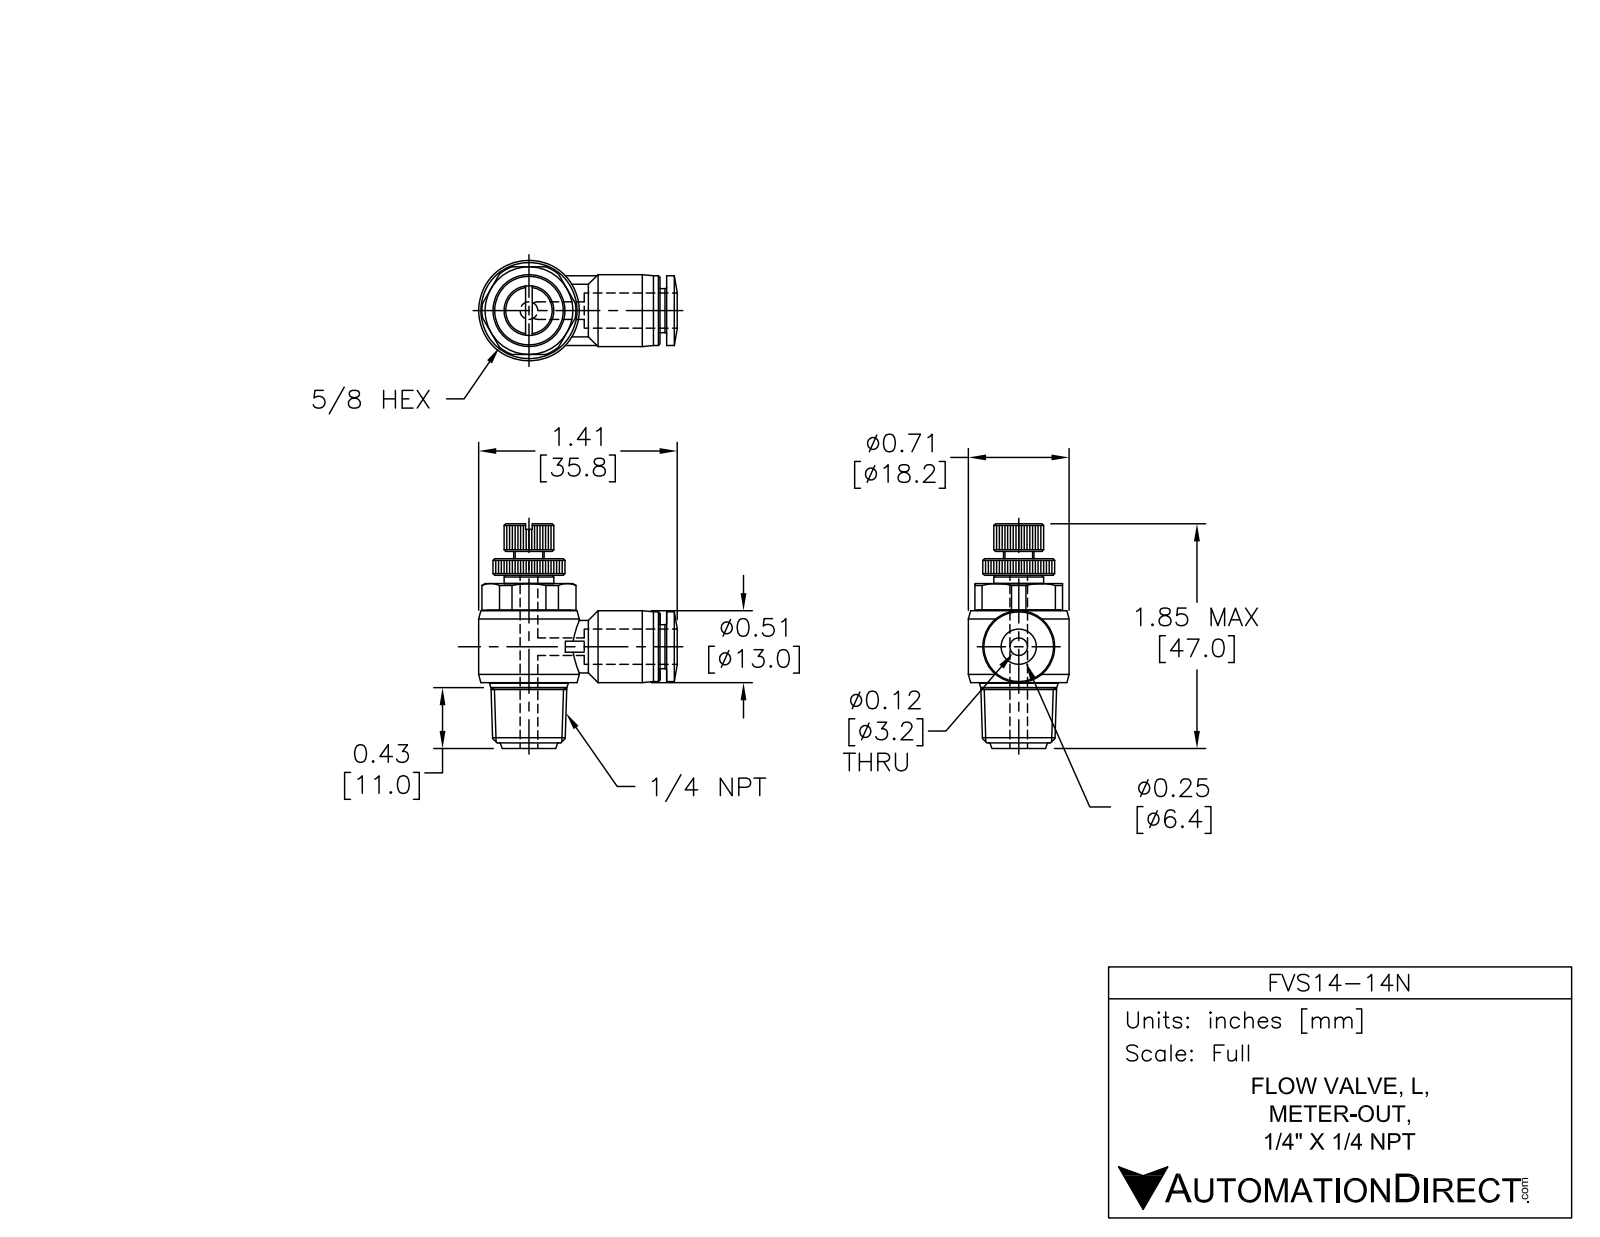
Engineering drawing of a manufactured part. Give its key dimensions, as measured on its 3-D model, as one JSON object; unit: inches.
{"part_name": "FVS14-14N", "step_written_by": "SolidWorks 2015 (AUTOMOTIVE_DESIGN)", "units": "inches", "bodies": {"solids": 1, "faces": 424, "planar": 186, "cylindrical": 112, "other": 126}, "overall_size": [1.85, 1.413, 0.717], "volume_in3": 0.49, "surface_area_in2": 6.727, "round_holes": [[0.177, 2], [0.258, 1]], "round_bosses_or_shafts": [[0.717, 1], [0.591, 1], [0.539, 1], [0.512, 1], [0.496, 1], [0.374, 1], [0.354, 1], [0.313, 1]], "partial_cylinders_radius": [[0.256, 1], [0.335, 1]], "face_to_face_distances": [0.177, 0.705, 0.882, 0.624, 0.764, 0.469, 0.047, 0.37, 0.059, 0.118]}
